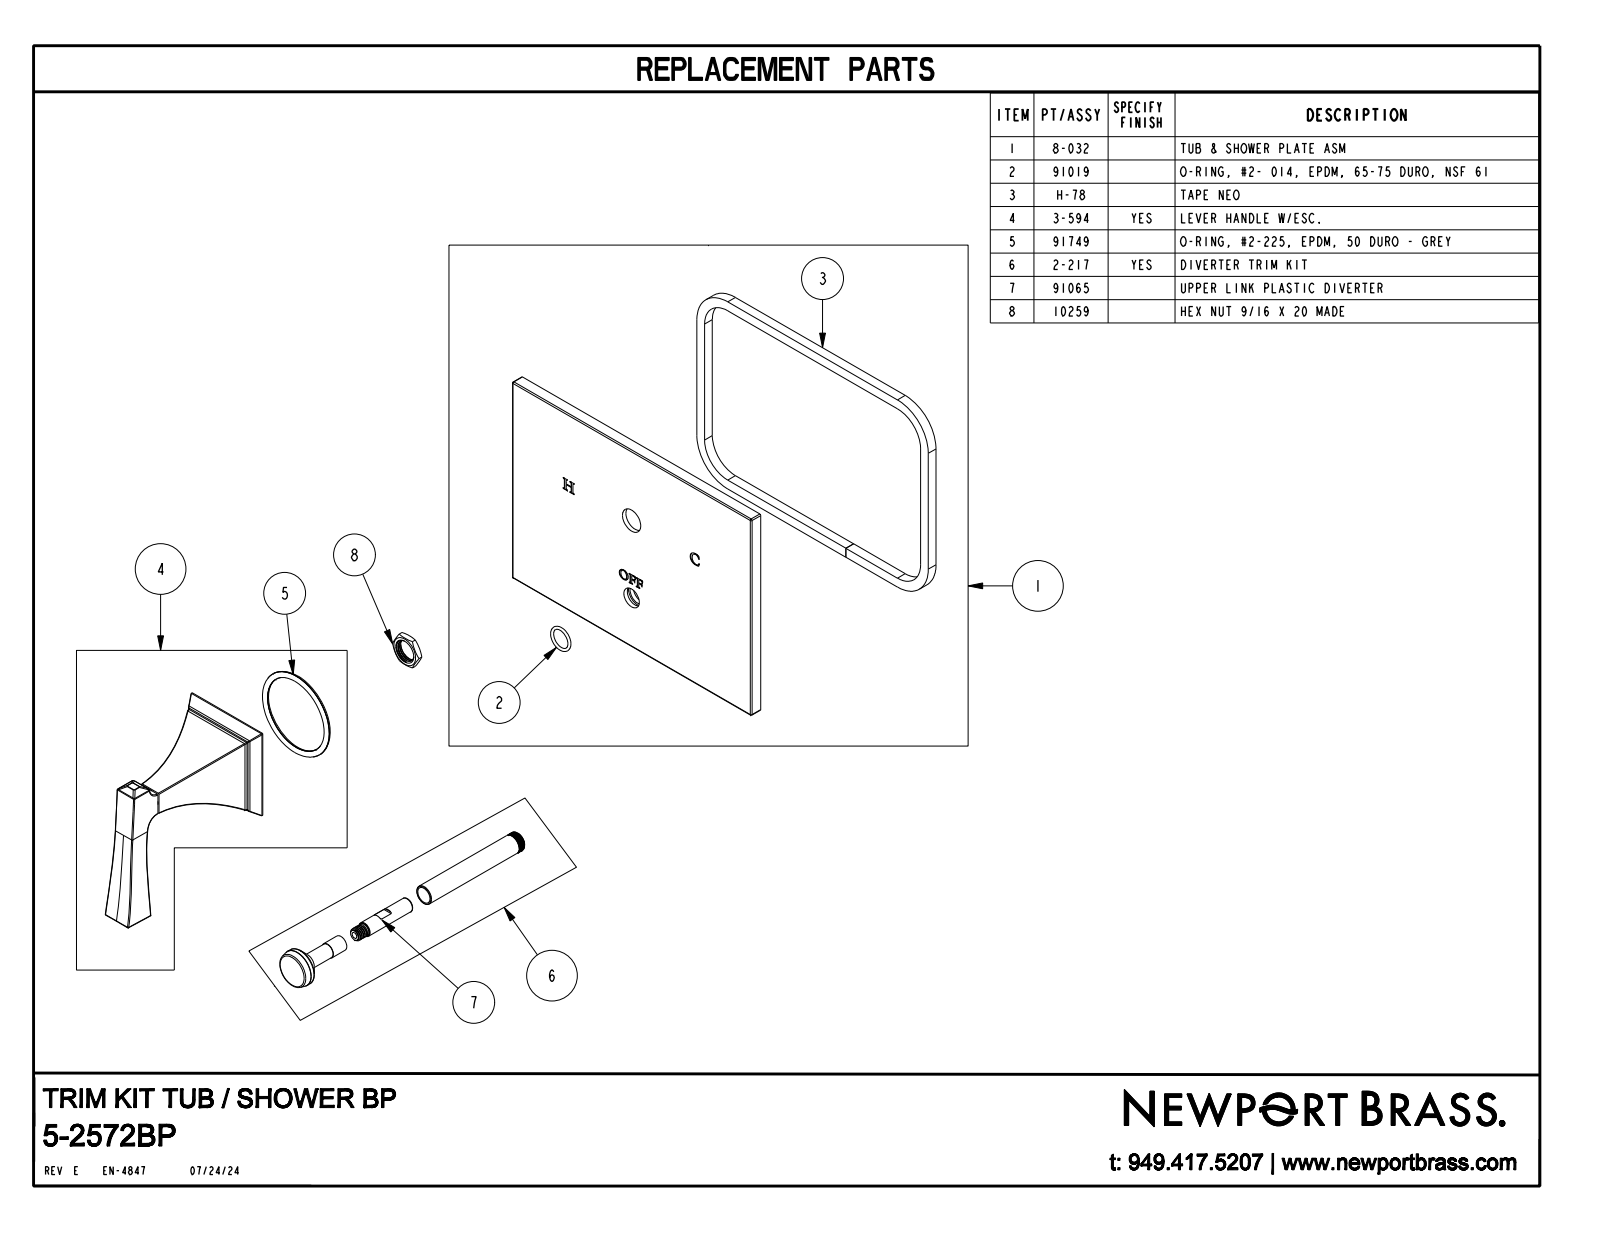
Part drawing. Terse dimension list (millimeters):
name: 5-2572BP
written by: CREO PARAMETRIC BY PTC INC, 2018400 (CONFIG_CONTROL_DESIGN)
unit: mm
bodies: 1 solid, 406 faces (63 planar, 40 cylindrical, 303 other)
size: 196.9 × 139.7 × 99.2
volume: 311 800 mm³; area: 72 970 mm²
bosses: 1× ⌀22.9, 1× ⌀12.9, 1× ⌀12, 1× ⌀9
rounds: 16× R0.5, 8× R0.8, 8× R1.5
face distances: 7.9, 139.7, 196.9, 91.3, 105.5, 14.2, 40.2, 32.3, 7.5, 0.4
